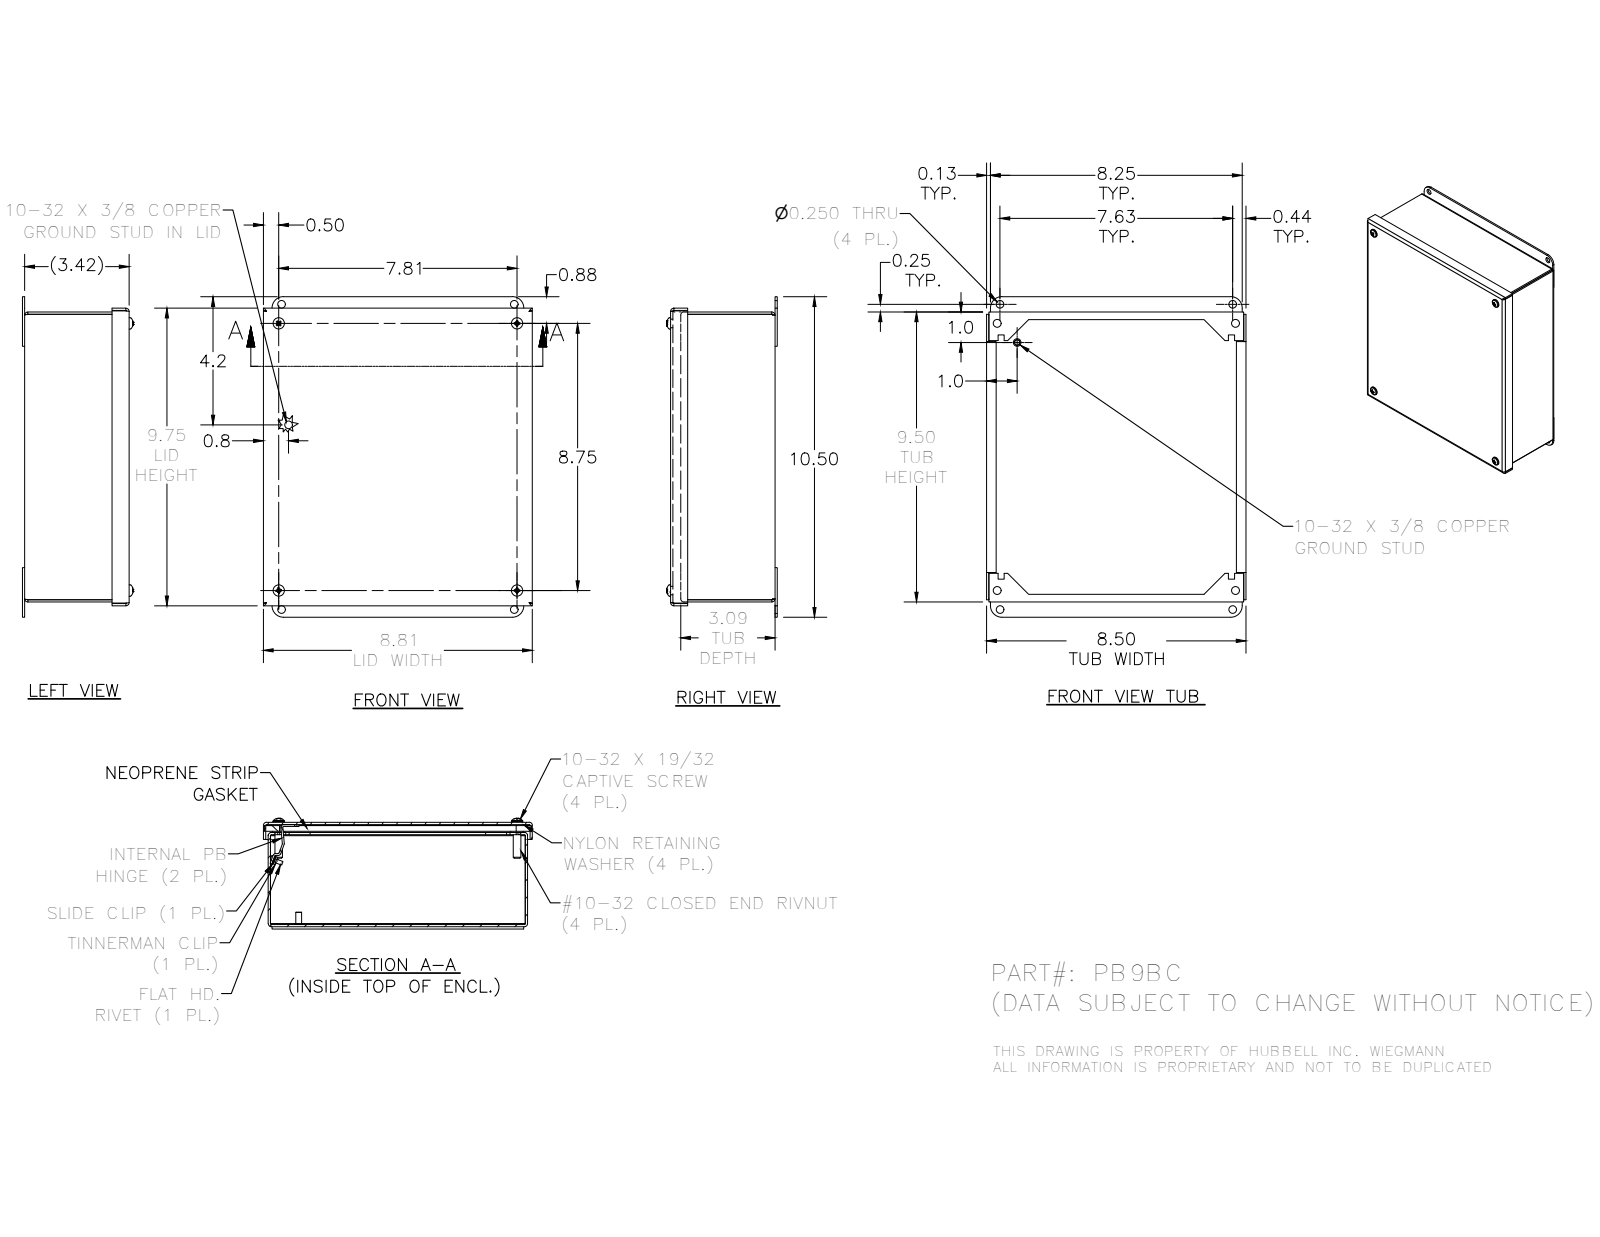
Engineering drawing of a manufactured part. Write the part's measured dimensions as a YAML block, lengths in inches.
part_name: "3285; 39077; 316244; 31817 (+8 more)"
step_written_by: "Autodesk Inventor 2016 (AUTOMOTIVE_DESIGN)"
units: inches
bodies: {solids: 25, faces: 609, planar: 363, cylindrical: 132, other: 114}
overall_size: [10.5, 8.813, 3.626]
volume: 28.4
surface_area: 734.3
round_holes:
  - {diameter: 0.156, count: 4}
  - {diameter: 0.196, count: 4}
  - {diameter: 0.25, count: 4}
  - {diameter: 0.257, count: 4}
  - {diameter: 0.278, count: 4}
  - {diameter: 0.281, count: 4}
  - {diameter: 0.313, count: 4}
  - {diameter: 0.14, count: 2}
round_bosses_or_shafts:
  - {diameter: 0.19, count: 6}
  - {diameter: 0.453, count: 4}
  - {diameter: 0.406, count: 4}
  - {diameter: 0.373, count: 4}
  - {diameter: 0.248, count: 4}
  - {diameter: 0.25, count: 3}
  - {diameter: 0.125, count: 1}
partial_cylinders:
  - {radius: 0.031, count: 12}
  - {radius: 0.105, count: 12}
  - {radius: 0.188, count: 6}
  - {radius: 0.089, count: 4}
  - {radius: 0.09, count: 4}
  - {radius: 0.375, count: 4}
  - {radius: 0.031, count: 3}
  - {radius: 0.063, count: 3}
face_to_face_distances: [0.074, 3.348, 3.422, 3.274, 8.426, 8.5, 8.352, 0.148, 3.496, 0.032]
hole_center_spacings: [8.75, 11.729, 12.143, 0.632, 8.749, 9.375, 9.376, 11.73]
